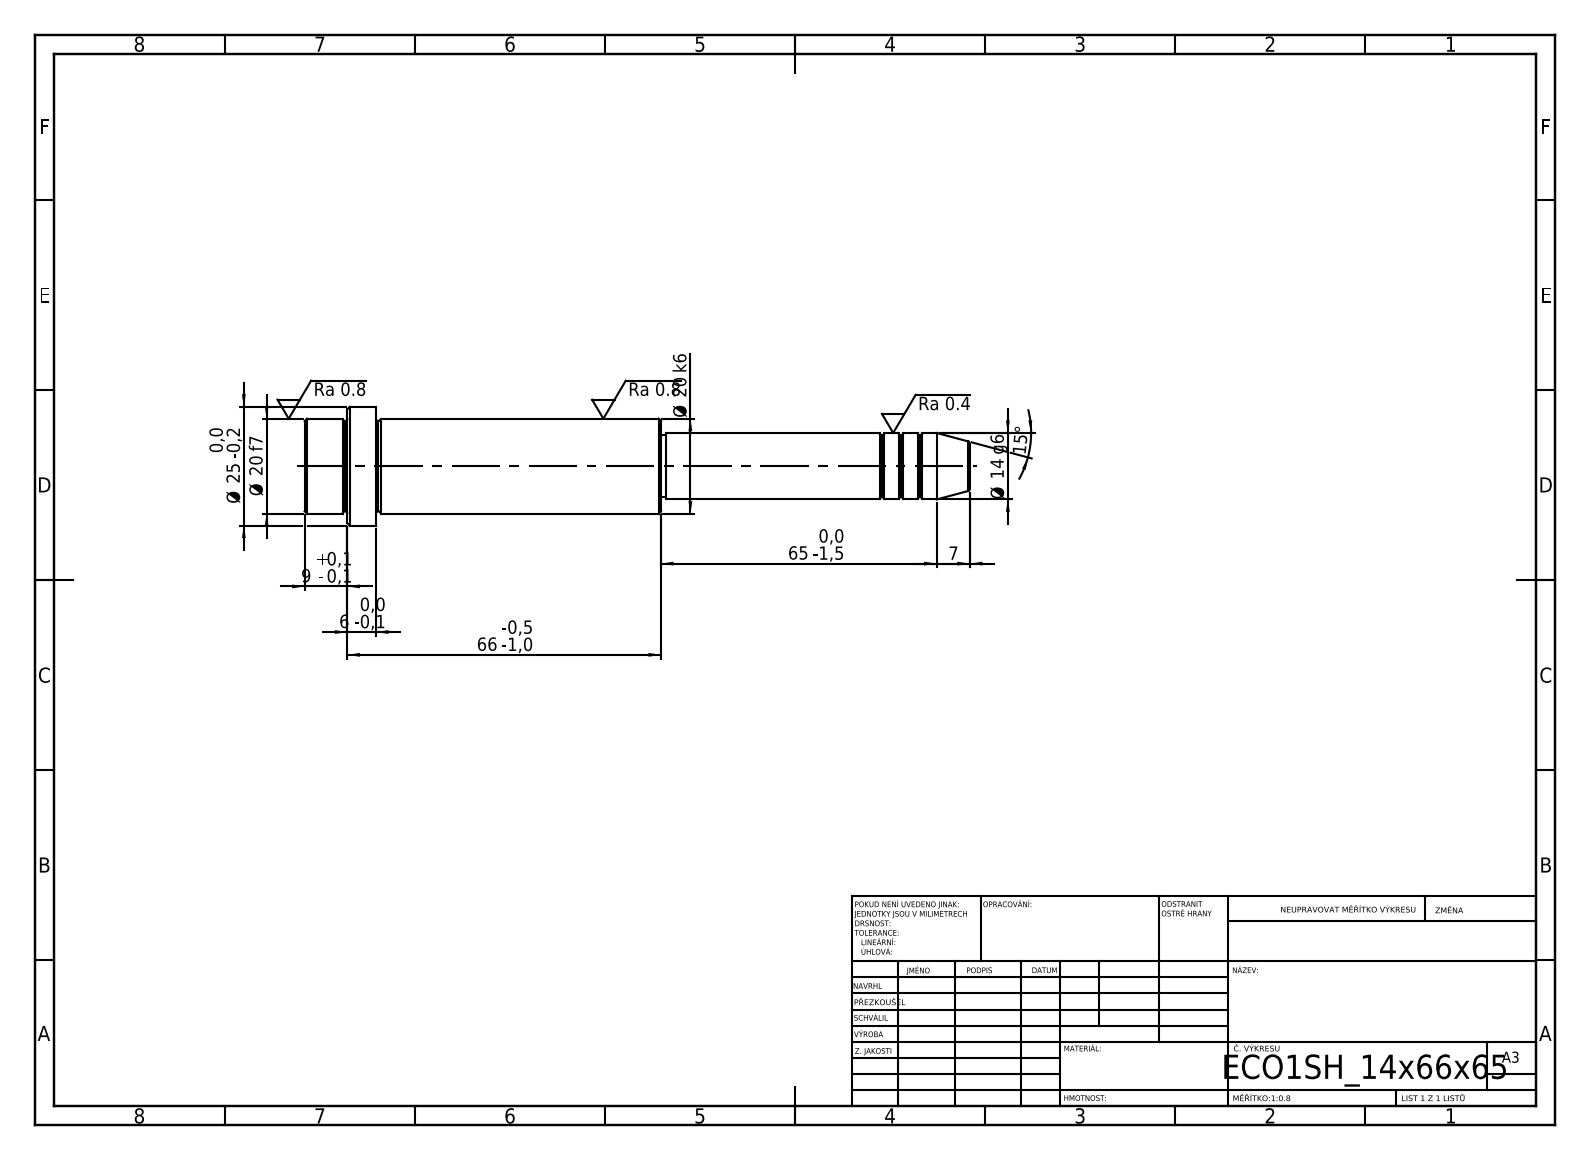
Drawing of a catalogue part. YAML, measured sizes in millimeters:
step_written_by: "SolidWorks 2019 (CONFIG_CONTROL_DESIGN)"
units: millimeters
bodies: {solids: 1, faces: 52, planar: 6, cylindrical: 16, other: 30}
overall_size: [140, 25, 25]
volume: 34219
surface_area: 8650
round_bosses_or_shafts:
  - {diameter: 25, count: 1}
  - {diameter: 20, count: 1}
  - {diameter: 14, count: 1}
  - {diameter: 13, count: 1}
face_to_face_distances: [15, 60, 75, 66, 6, 9, 65, 125, 131, 140]
